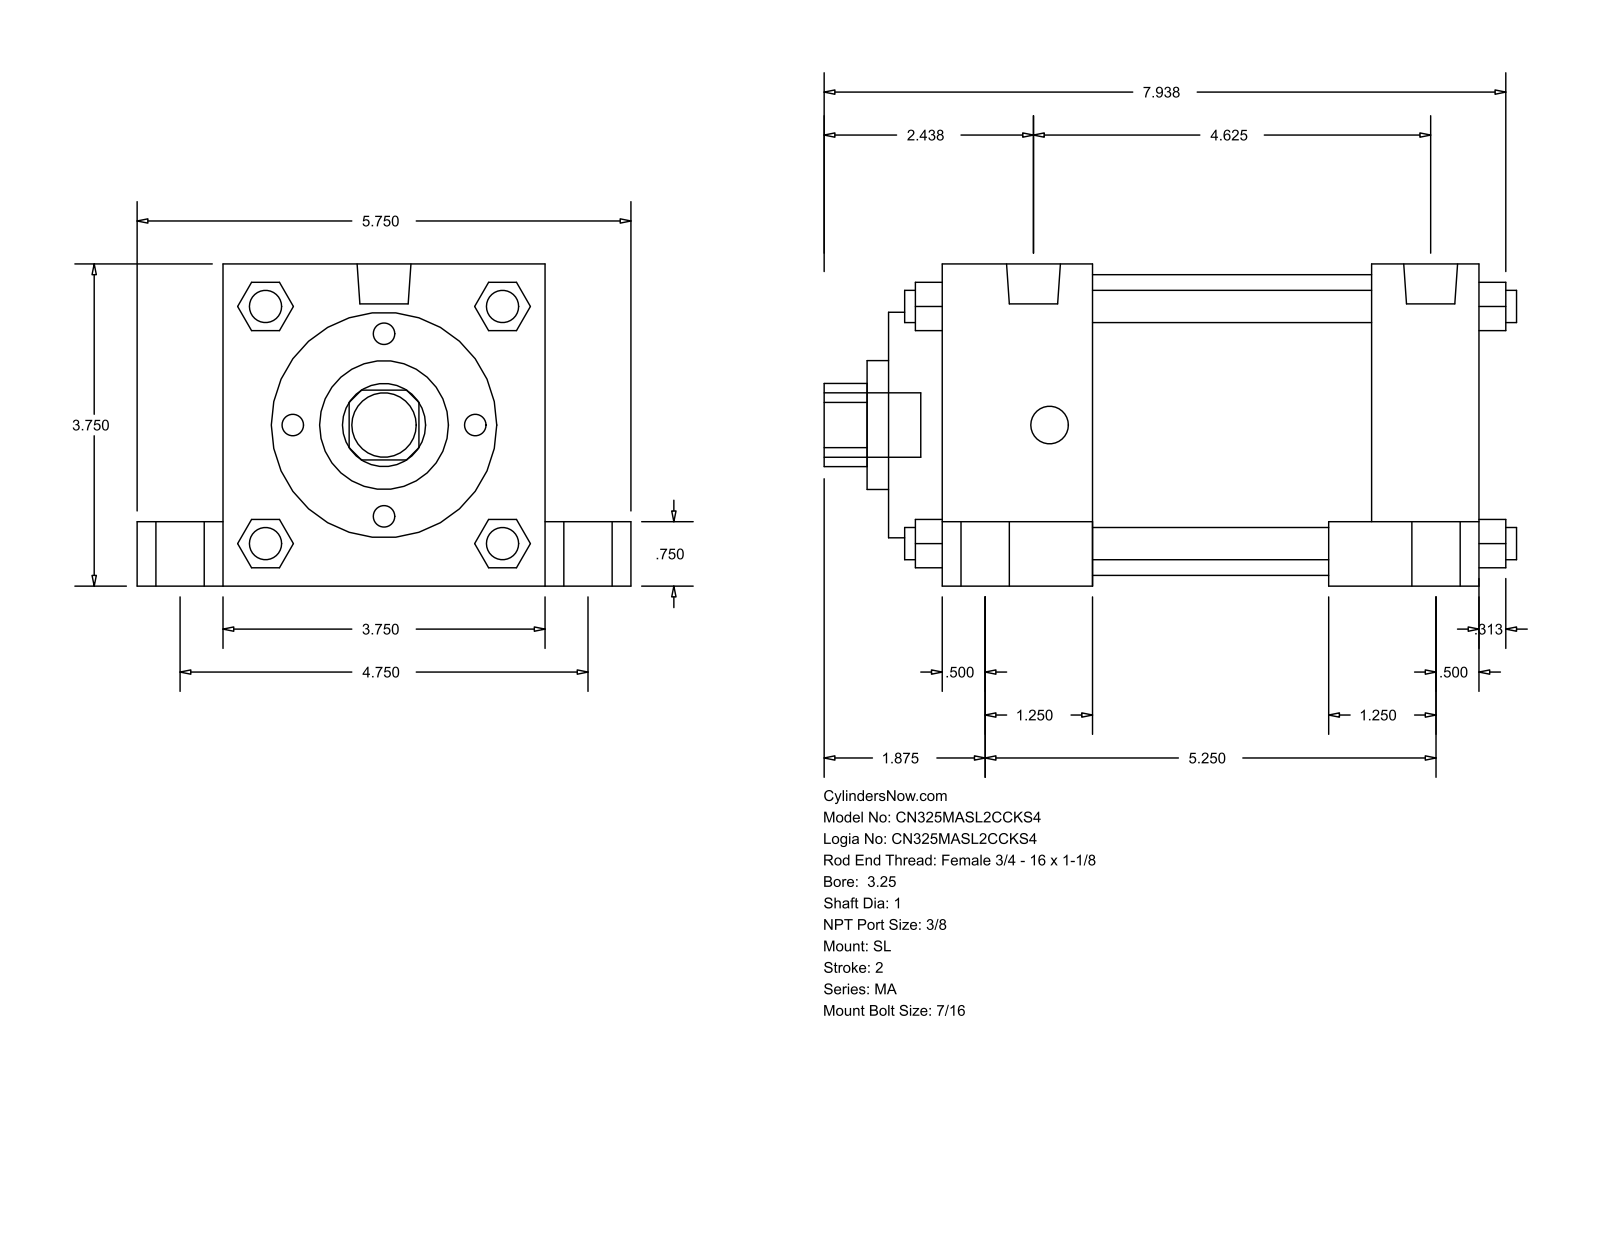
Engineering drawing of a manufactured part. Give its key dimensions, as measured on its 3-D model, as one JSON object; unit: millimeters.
{"part_name": "MA_SL__0325_1", "step_written_by": "GSSL Pune (CONFIG_CONTROL_DESIGN)", "units": "millimeters", "bodies": {"solids": 0, "faces": 150, "planar": 113, "cylindrical": 37, "other": 0}, "overall_size": [204.79, 146.05, 95.25], "round_holes": [[25.4, 1], [38.1, 1], [66.67, 1], [88.9, 1]], "round_bosses_or_shafts": [[20.64, 4], [14.29, 4], [11.11, 4], [9.53, 4], [15.93, 2], [19.05, 1]], "partial_cylinders_radius": [[12.29, 1]], "face_to_face_distances": [95.24, 158.76, 82.55, 15.87, 25.41, 120.65, 19.05, 127.01, 31.75, 44.46]}
